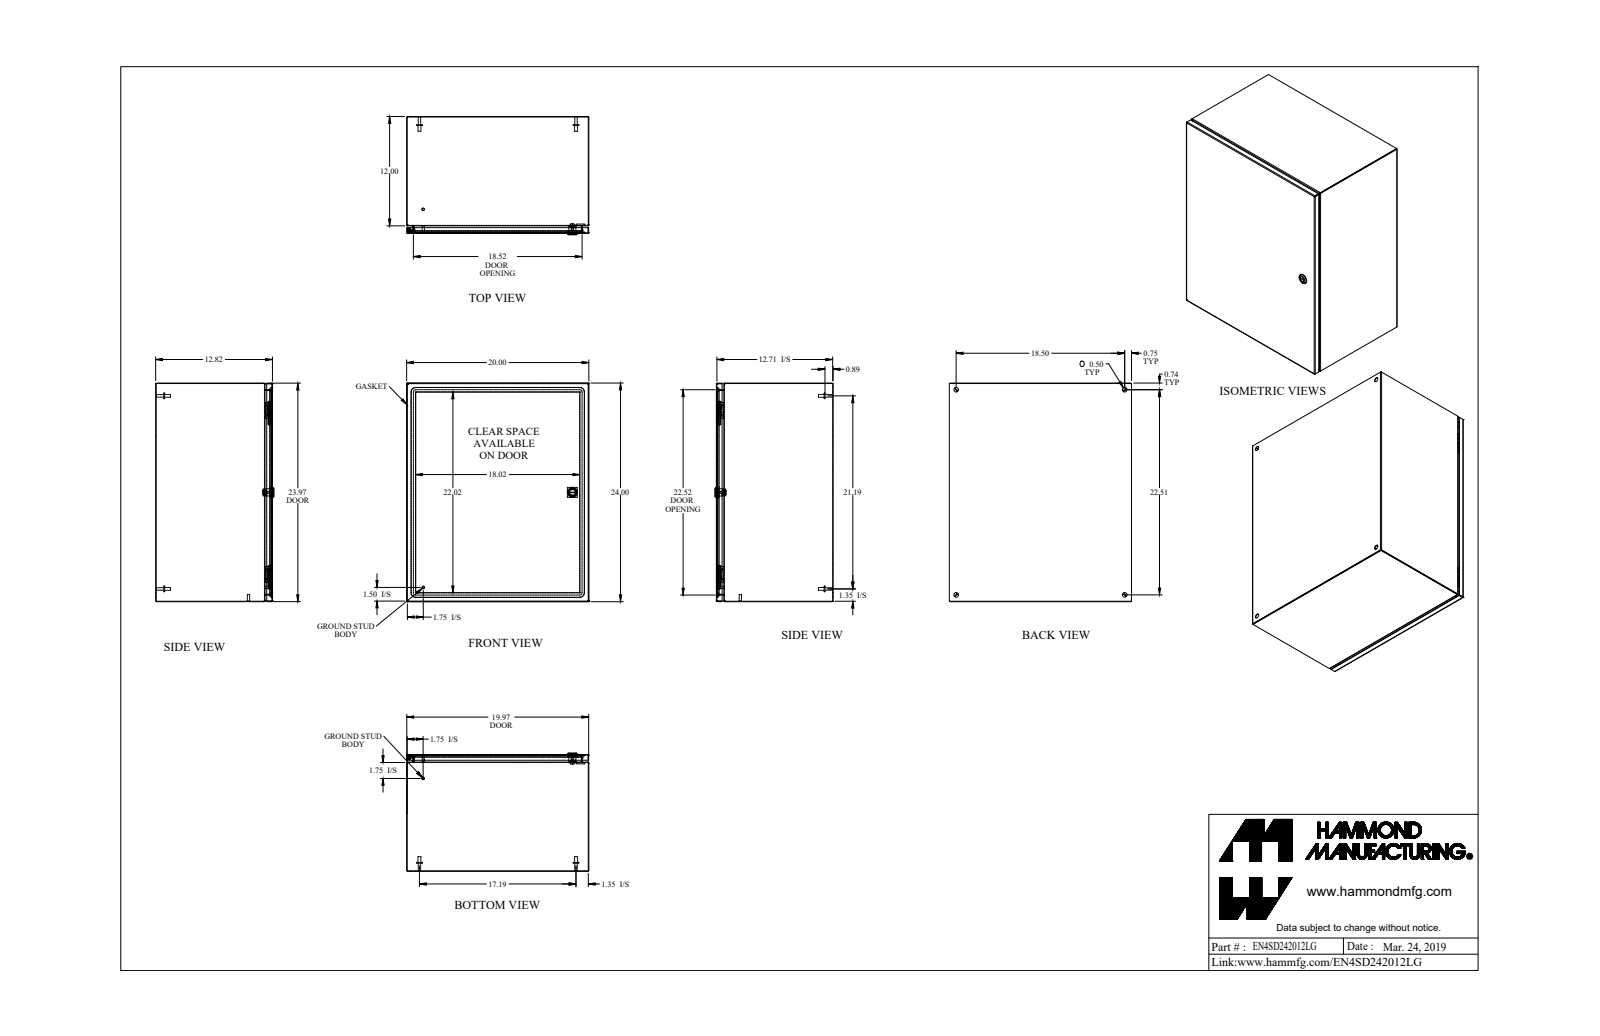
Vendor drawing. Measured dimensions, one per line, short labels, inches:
name: EN4SD242012LG
written by: SolidWorks 2019 (AUTOMOTIVE_DESIGN)
unit: in
bodies: 23 solids, 591 faces (266 planar, 201 cylindrical, 124 other)
size: 24 × 20 × 12.982
volume: 140.8 in³; area: 4 568 in²
holes: 4× ⌀0.5, 1× ⌀0.172, 1× ⌀0.232, 1× ⌀0.24, 1× ⌀0.242, 1× ⌀0.625, 1× ⌀0.785
bosses: 4× ⌀0.625, 4× ⌀0.313, 4× ⌀0.27, 2× ⌀0.281, 2× ⌀0.25, 1× ⌀1.1, 1× ⌀0.525, 1× ⌀0.455
rounds: 15× R0.029, 15× R0.086, 12× R0.188, 8× R0.1, 4× R0.006, 4× R0.062, 4× R0.25, 4× R0.499
face distances: 0.057, 19.943, 0.072, 12.765, 12.693, 12.75, 23.943, 12.822, 19.886, 20
hole spacings: 18.5, 22.514, 29.14, 11.298, 11.315, 20.754, 20.763
